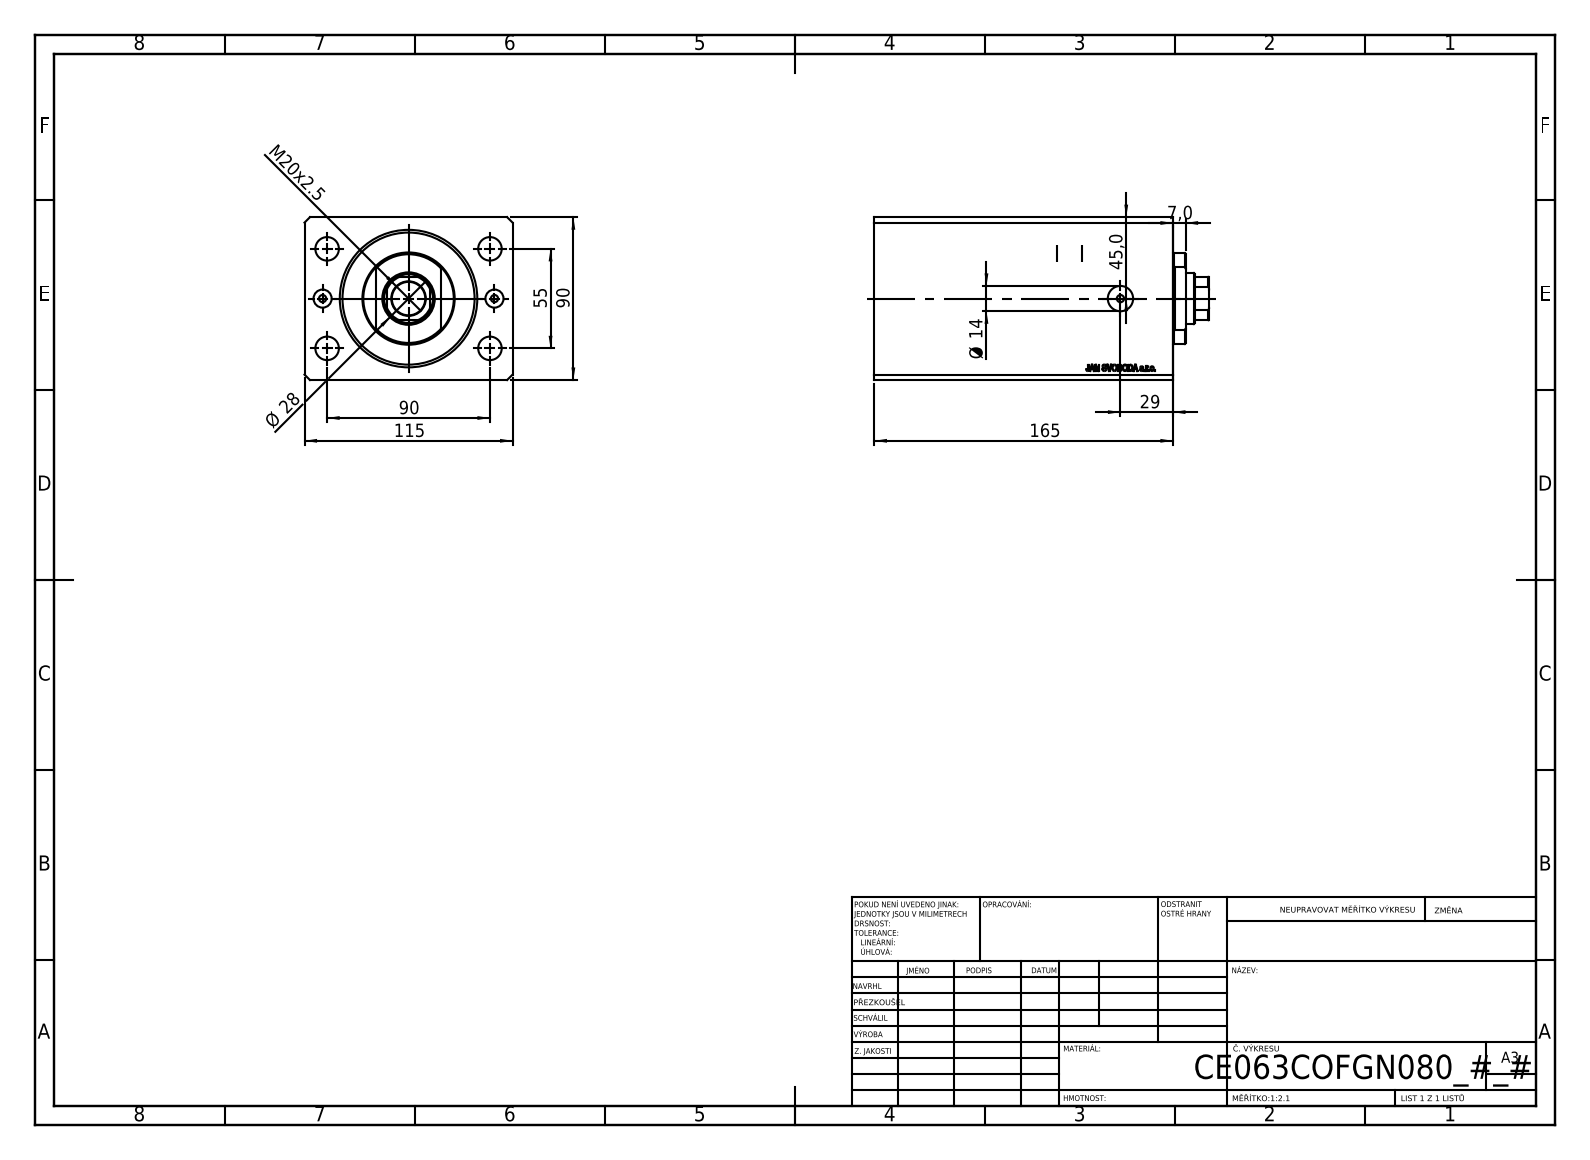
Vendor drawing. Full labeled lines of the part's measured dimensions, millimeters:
Part name (STEP PRODUCT): V250CE_C_VCP; V250CE_C_Body; V250CE_VC_C
STEP written by: SolidWorks 2019 (CONFIG_CONTROL_DESIGN)
Units: millimetres
Bodies: 3 solids, 864 faces (428 planar, 44 cylindrical, 392 other)
Overall size (bounding box): 185 × 115 × 90
Volume: 1 423 000 mm³ · Surface area: 189 045 mm²
Round holes (diameter × count): ⌀4 ×4, ⌀13 ×4, ⌀10 ×2, ⌀14 ×2, ⌀18.5 ×1, ⌀28 ×1, ⌀63 ×1, ⌀76 ×1
Round bosses / shafts (diameter × count): ⌀50 ×1
Partial cylindrical surfaces — rounded edges, fillets, slot ends (radius × count): R13.5 ×1
Main face-to-face distances: 90, 115, 165, 17.9, 147.1, 20, 145, 127.1, 65, 80
Hole centre spacings: 27.61, 52.74, 96.5, 47.5, 55, 90, 105.48, 95
